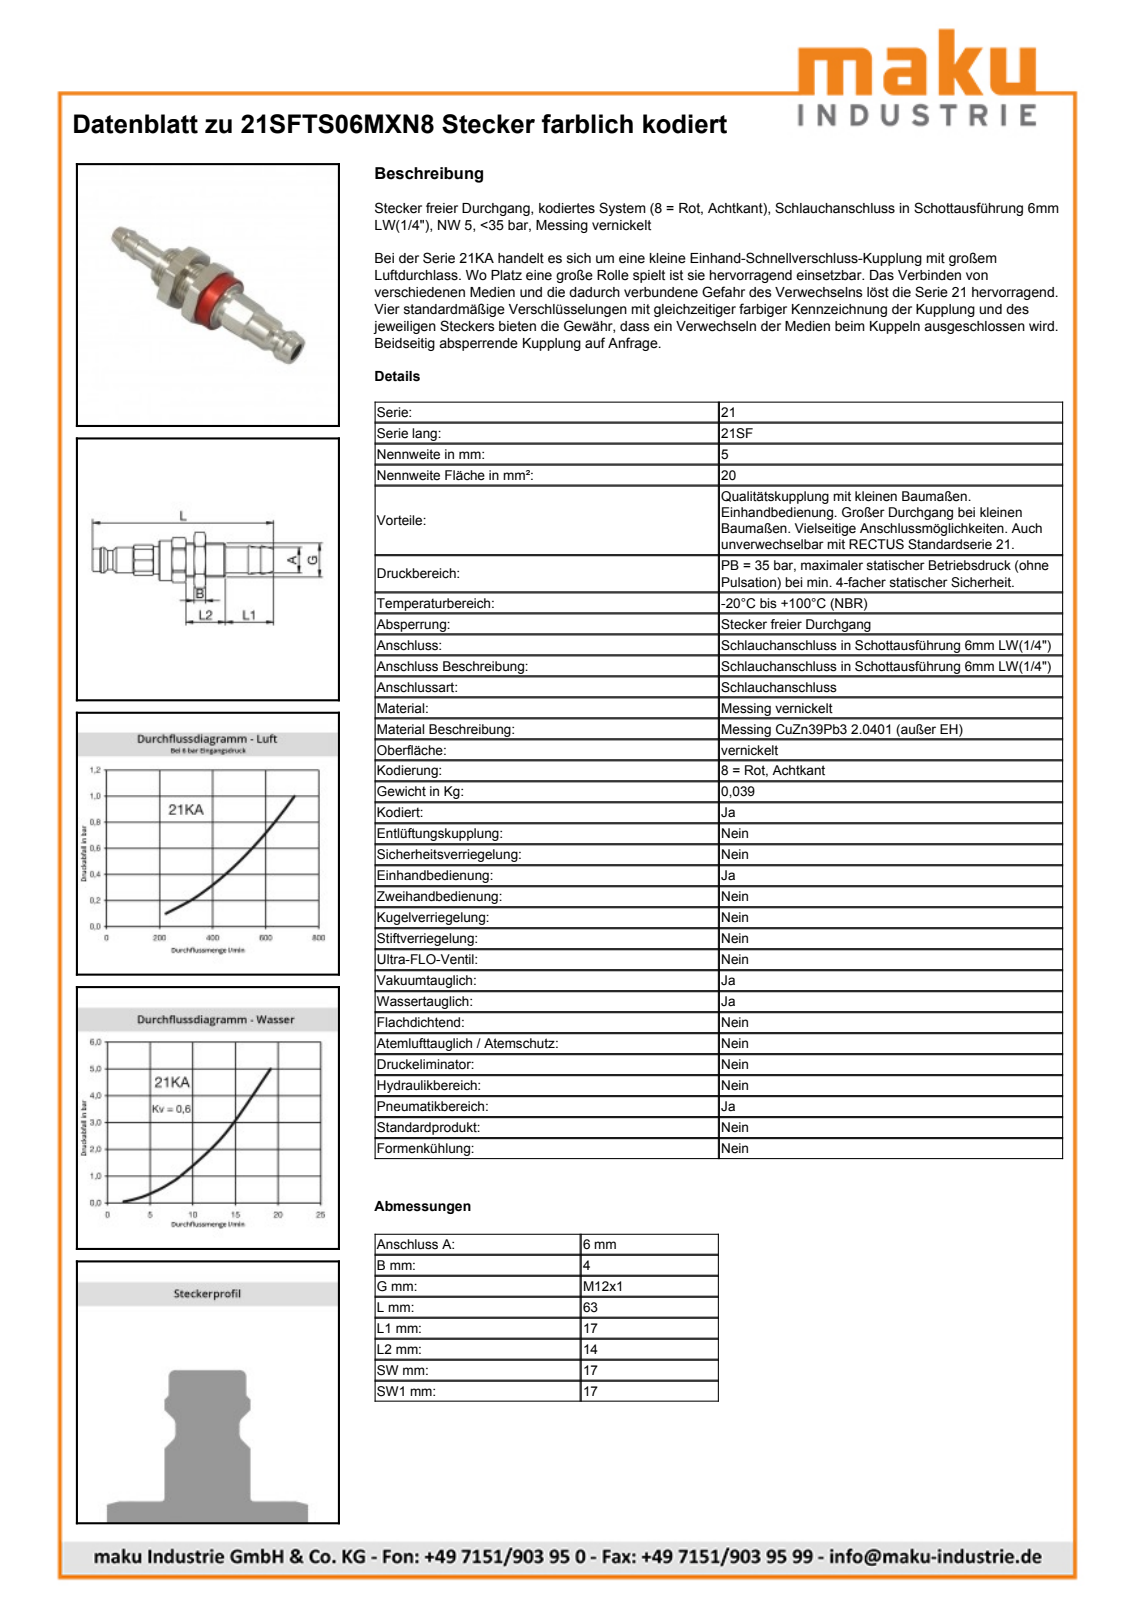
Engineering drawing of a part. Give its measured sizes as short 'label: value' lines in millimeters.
name: D107703; D107687; D104296; D103012
written by: Autodesk Inventor 2013 (AUTOMOTIVE_DESIGN)
unit: mm
bodies: 3 solids, 114 faces (32 planar, 35 cylindrical, 47 other)
size: 63 × 19.15 × 19.15
volume: 4 883 mm³; area: 4 400 mm²
holes: 1× ⌀4, 1× ⌀4.95, 1× ⌀12, 1× ⌀13.85, 1× ⌀14.05
bosses: 1× ⌀15.5, 1× ⌀14, 1× ⌀10.6, 1× ⌀9.7, 1× ⌀9, 1× ⌀8.1, 1× ⌀6.65, 1× ⌀6.05
rounds: 1× R5.35, 1× R9.57
face distances: 17, 4, 8.48, 10, 12.48, 4.48, 4.5, 16.98, 12.98, 8.5
